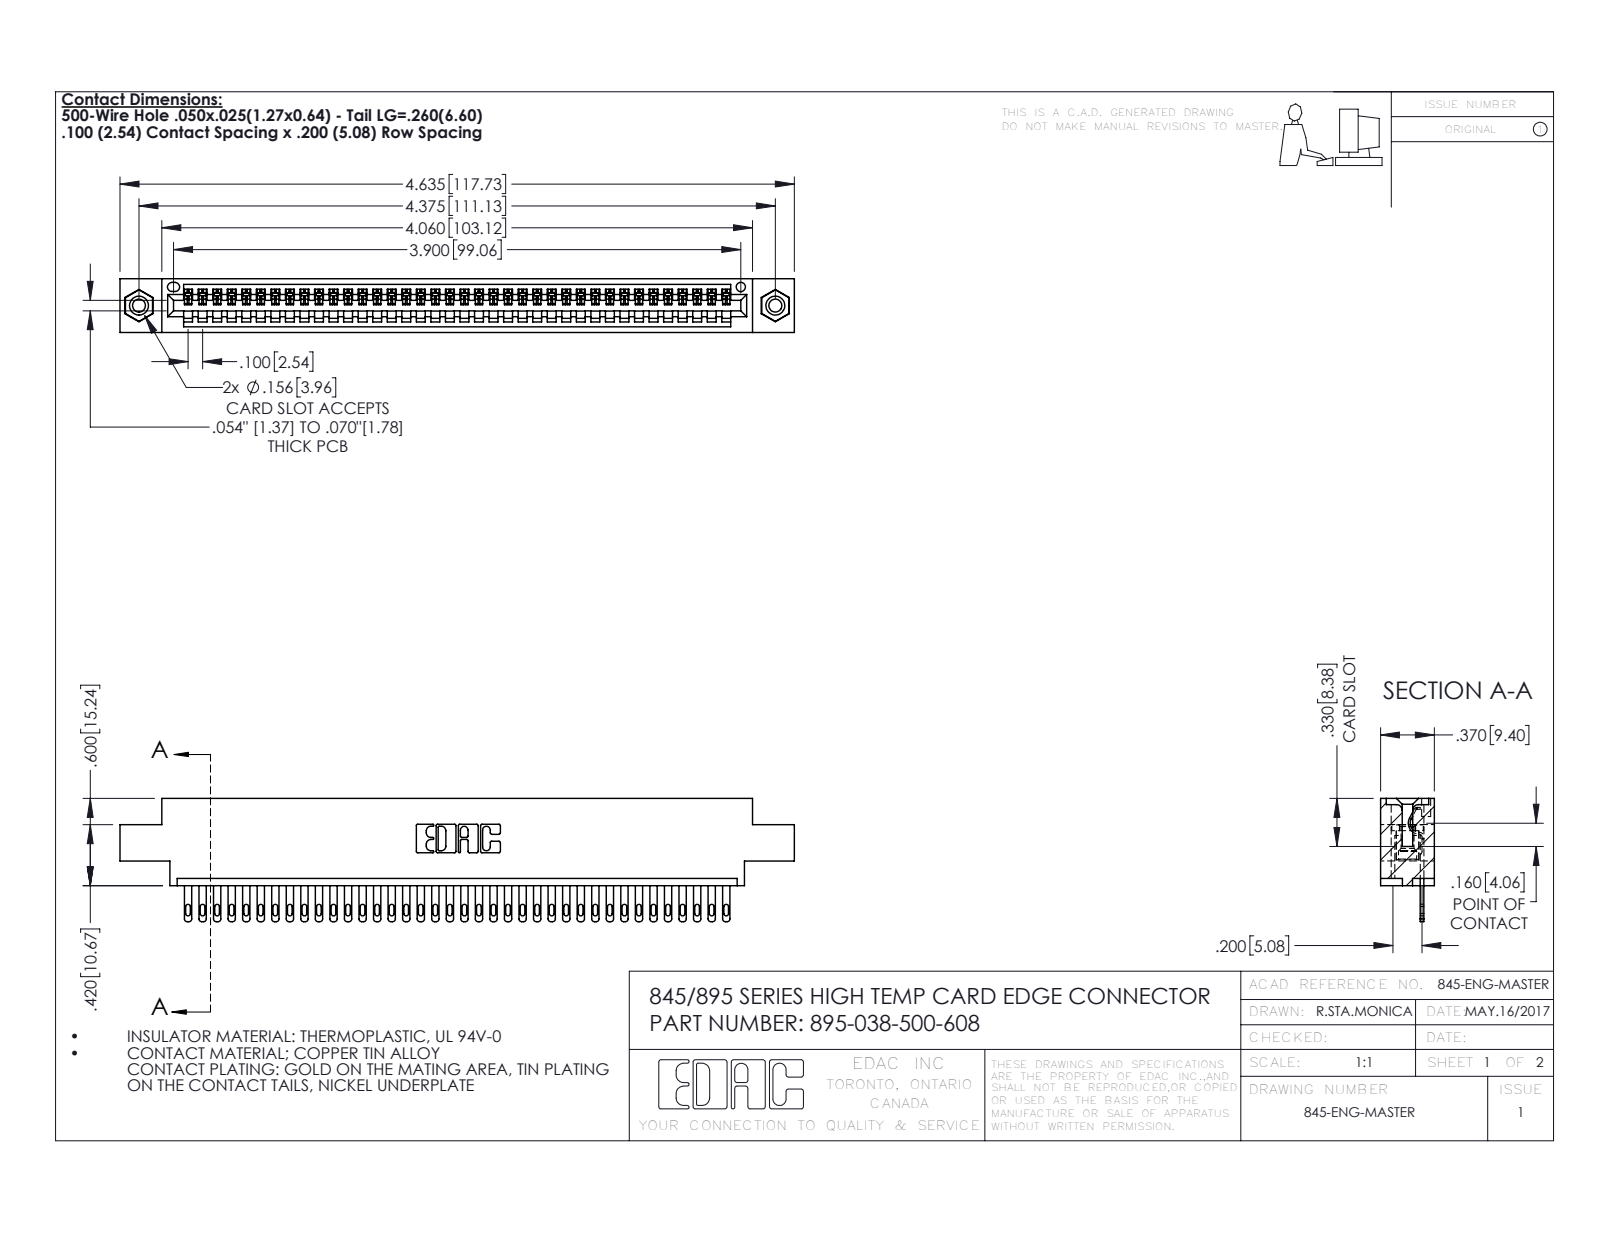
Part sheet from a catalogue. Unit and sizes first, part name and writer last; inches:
Units: inches
Overall size (bounding box): 4.635 × 0.847 × 0.37
Round holes (diameter × count): ⌀0.089 ×2, ⌀0.125 ×2, ⌀0.156 ×2, ⌀0.064 ×1
Round bosses / shafts (diameter × count): ⌀0.155 ×2
Partial cylindrical surfaces — rounded edges, fillets, slot ends (radius × count): R0.006 ×76, R0.016 ×76, R0.02 ×76, R0.01 ×22, R0.007 ×6, R0.031 ×6, R0.026 ×3, R0.031 ×2
Main face-to-face distances: 0.072, 0.298, 0.37, 0.098, 0.272, 0.025, 0.2, 0.225, 0.175, 0.149
Hole centre spacings: 0.27, 4.139, 4.375
Volume: 0.674 in³ · Surface area: 23.04 in²
Bodies: 41 solids, 2242 faces (1408 planar, 818 cylindrical, 16 other)
Part name (STEP PRODUCT): 345-250-001_345-250-003-102; 845 Part_0.170 Offset - 0.156 Dia-TI; 895-038-500-608; 345-292-001_345-293-100
STEP written by: SolidWorks 2020 (CONFIG_CONTROL_DESIGN)
